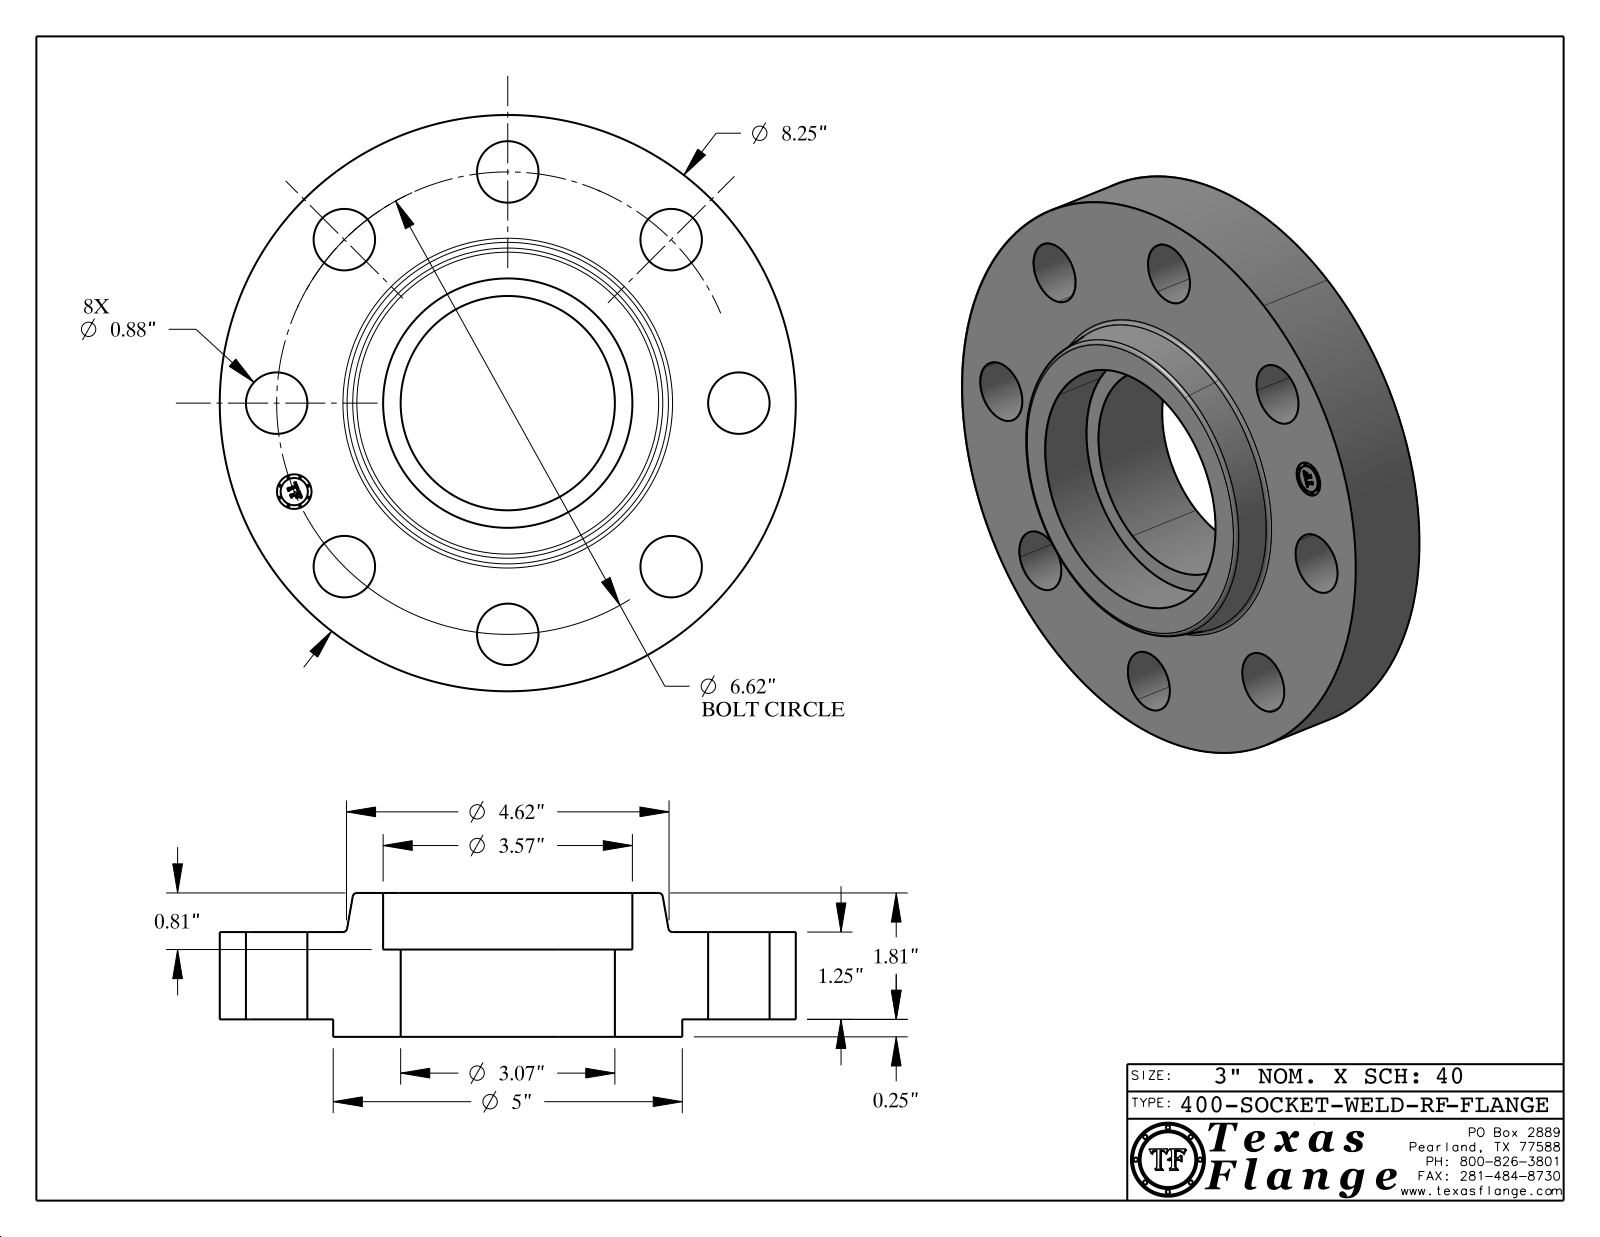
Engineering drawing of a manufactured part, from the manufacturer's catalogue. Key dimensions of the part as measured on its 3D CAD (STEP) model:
Part name (STEP PRODUCT): 400-SOCKET-WELD-RF
STEP written by: CATIA V5 STEP AP214 (AUTOMOTIVE_DESIGN)
Units: inches
Bodies: 1 solid, 420 faces (370 planar, 44 cylindrical, 6 other)
Overall size (bounding box): 8.25 × 8.25 × 2.06
Volume: 57.29 in³ · Surface area: 173.8 in²
Round holes (diameter × count): ⌀0.88 ×8, ⌀0.495 ×1, ⌀3.068 ×1, ⌀3.57 ×1
Round bosses / shafts (diameter × count): ⌀0.03 ×8, ⌀8.25 ×1, ⌀5 ×1, ⌀0.39 ×1
Main face-to-face distances: 1.25, 0.25, 1.5, 2.06, 1.81, 0.56, 1, 0.81, 0.015, 1.485
Hole centre spacings: 3.31, 2.533, 6.116, 4.681, 4.681, 1.291, 3.678, 6.493
